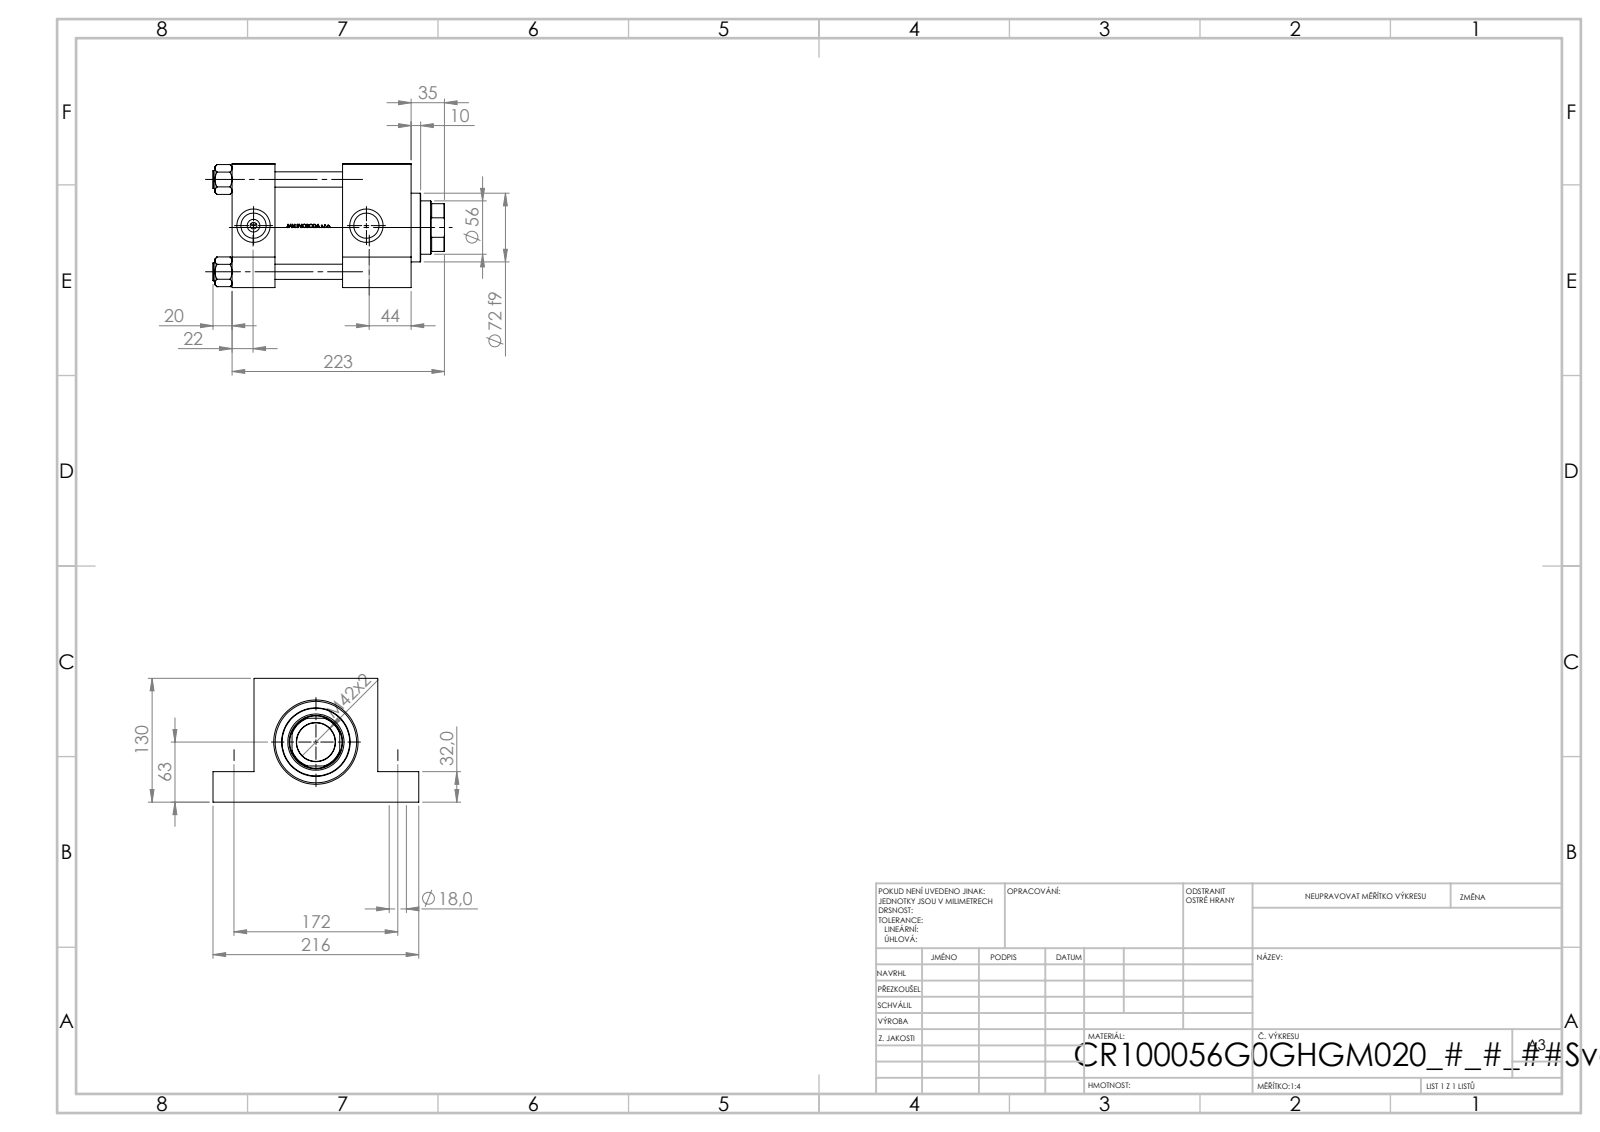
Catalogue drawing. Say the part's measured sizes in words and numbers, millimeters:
The part is named "NUT_M5_G; V215_VC_A; V215CR_G_TYCINKA; V215CR_VCP_G (+1 more)". Its 3-D file was written by "SolidWorks 2019 (CONFIG_CONTROL_DESIGN)". It is 11 solids with 1135 faces: 479 planar, 124 cylindrical and 532 other. Overall it measures 243 by 216 by 130 millimeters. Its volume is 2 789 000 cubic millimeters and its surface area 363 707 square millimeters. Round holes: 4 of diameter 16, 4 of diameter 18, 2 of diameter 7, 2 of diameter 26.44, 2 of diameter 35, 1 of diameter 40.5, 1 of diameter 56, 1 of diameter 59, 1 of diameter 76, 1 of diameter 85.5, 1 of diameter 100. Round bosses or shafts: 4 of diameter 19, 1 of diameter 106, 1 of diameter 72. Partial cylindrical surfaces (rounded edges, fillets, slot ends): 1 of radius 27. The main face-to-face distances are 130, 45, 188, 143, 116, 71, 72, 32, 98, 43. The hole center spacings are 96.9, 67.12, 69.95, 122, 137.04, 172, 210.87, 118.5.
